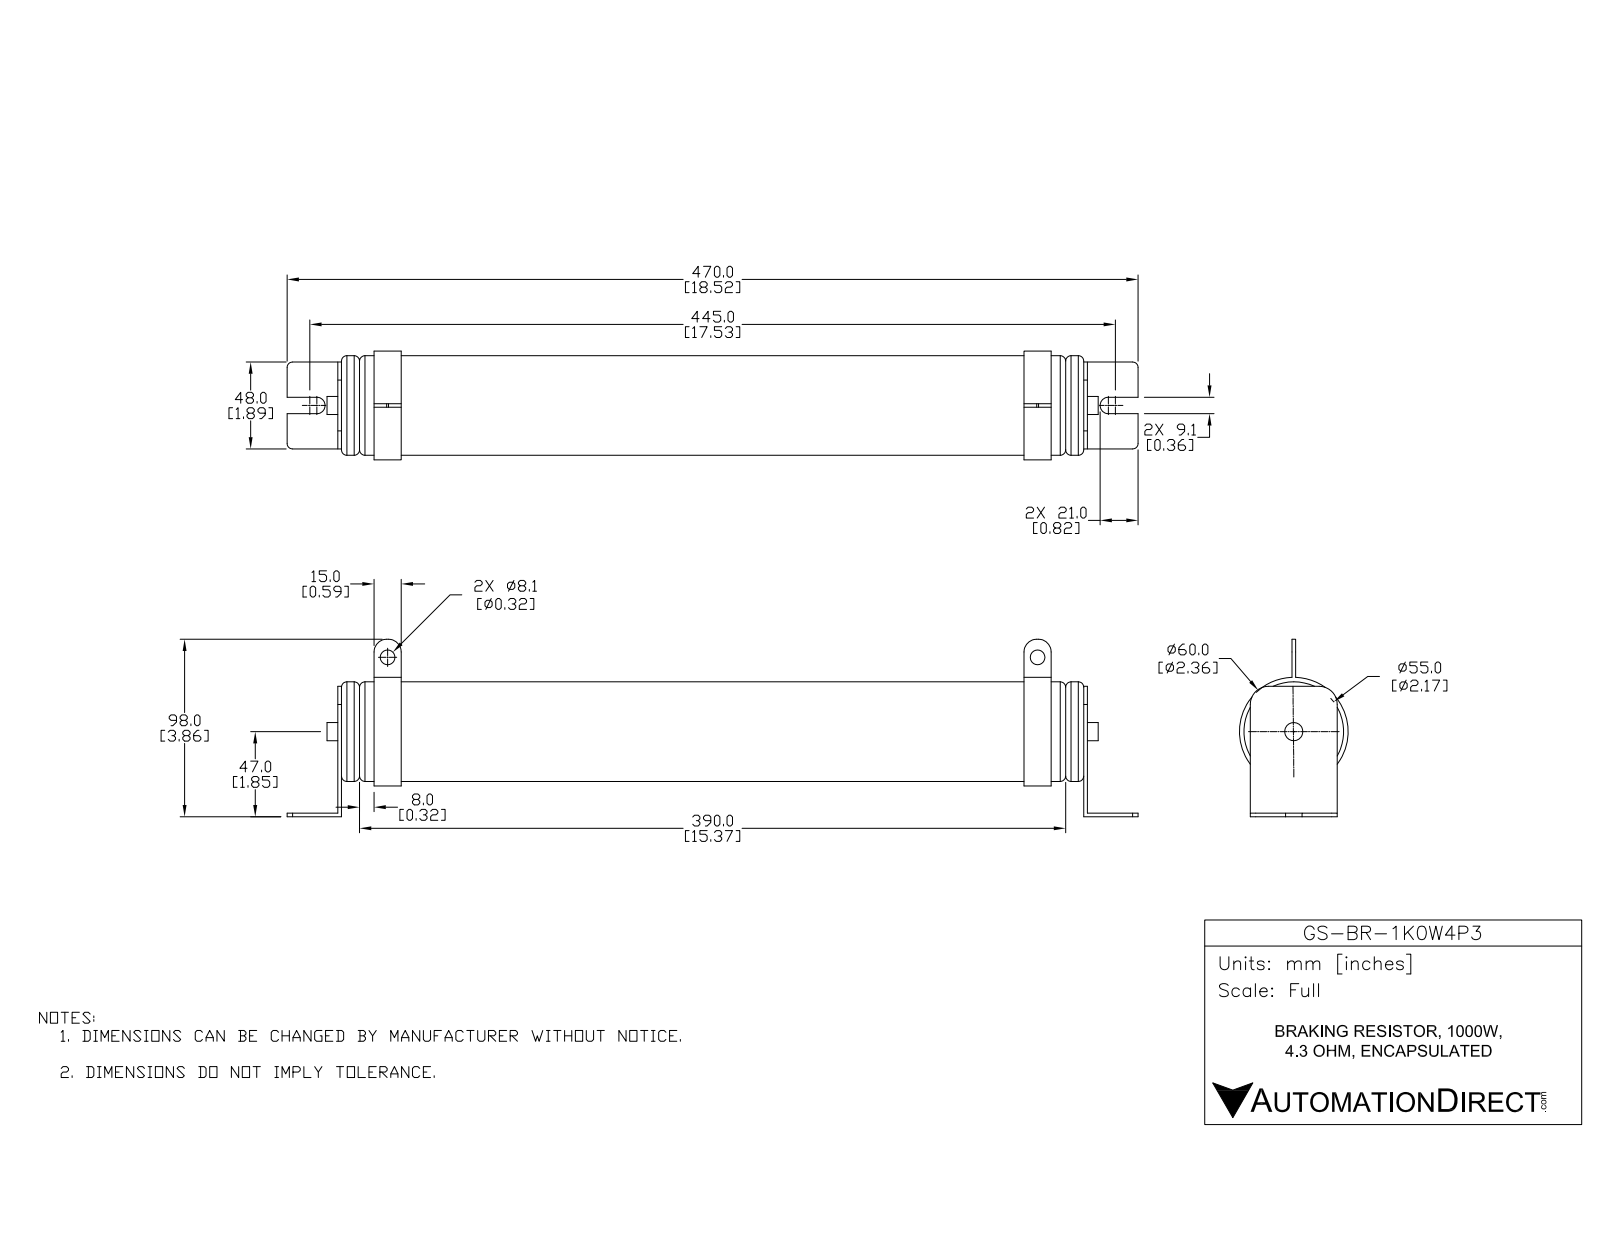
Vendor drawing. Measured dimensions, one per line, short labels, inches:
name: GS-BR-1K0W4P3
written by: SolidWorks 2015 (AUTOMOTIVE_DESIGN)
unit: in
bodies: 2 solids, 91 faces (41 planar, 38 cylindrical, 12 other)
size: 18.504 × 3.858 × 2.362
volume: 61.39 in³; area: 143.2 in²
holes: 2× ⌀0.319
bosses: 1× ⌀2.362, 1× ⌀2.166, 1× ⌀2.165, 1× ⌀0.394
rounds: 4× R0.118, 4× R0.276, 2× R0.179, 2× R0.394
face distances: 0.079, 16.299, 16.22, 16.142, 1.378, 14.921, 1.299, 14.843, 0.787, 15.512
hole spacings: 14.134
